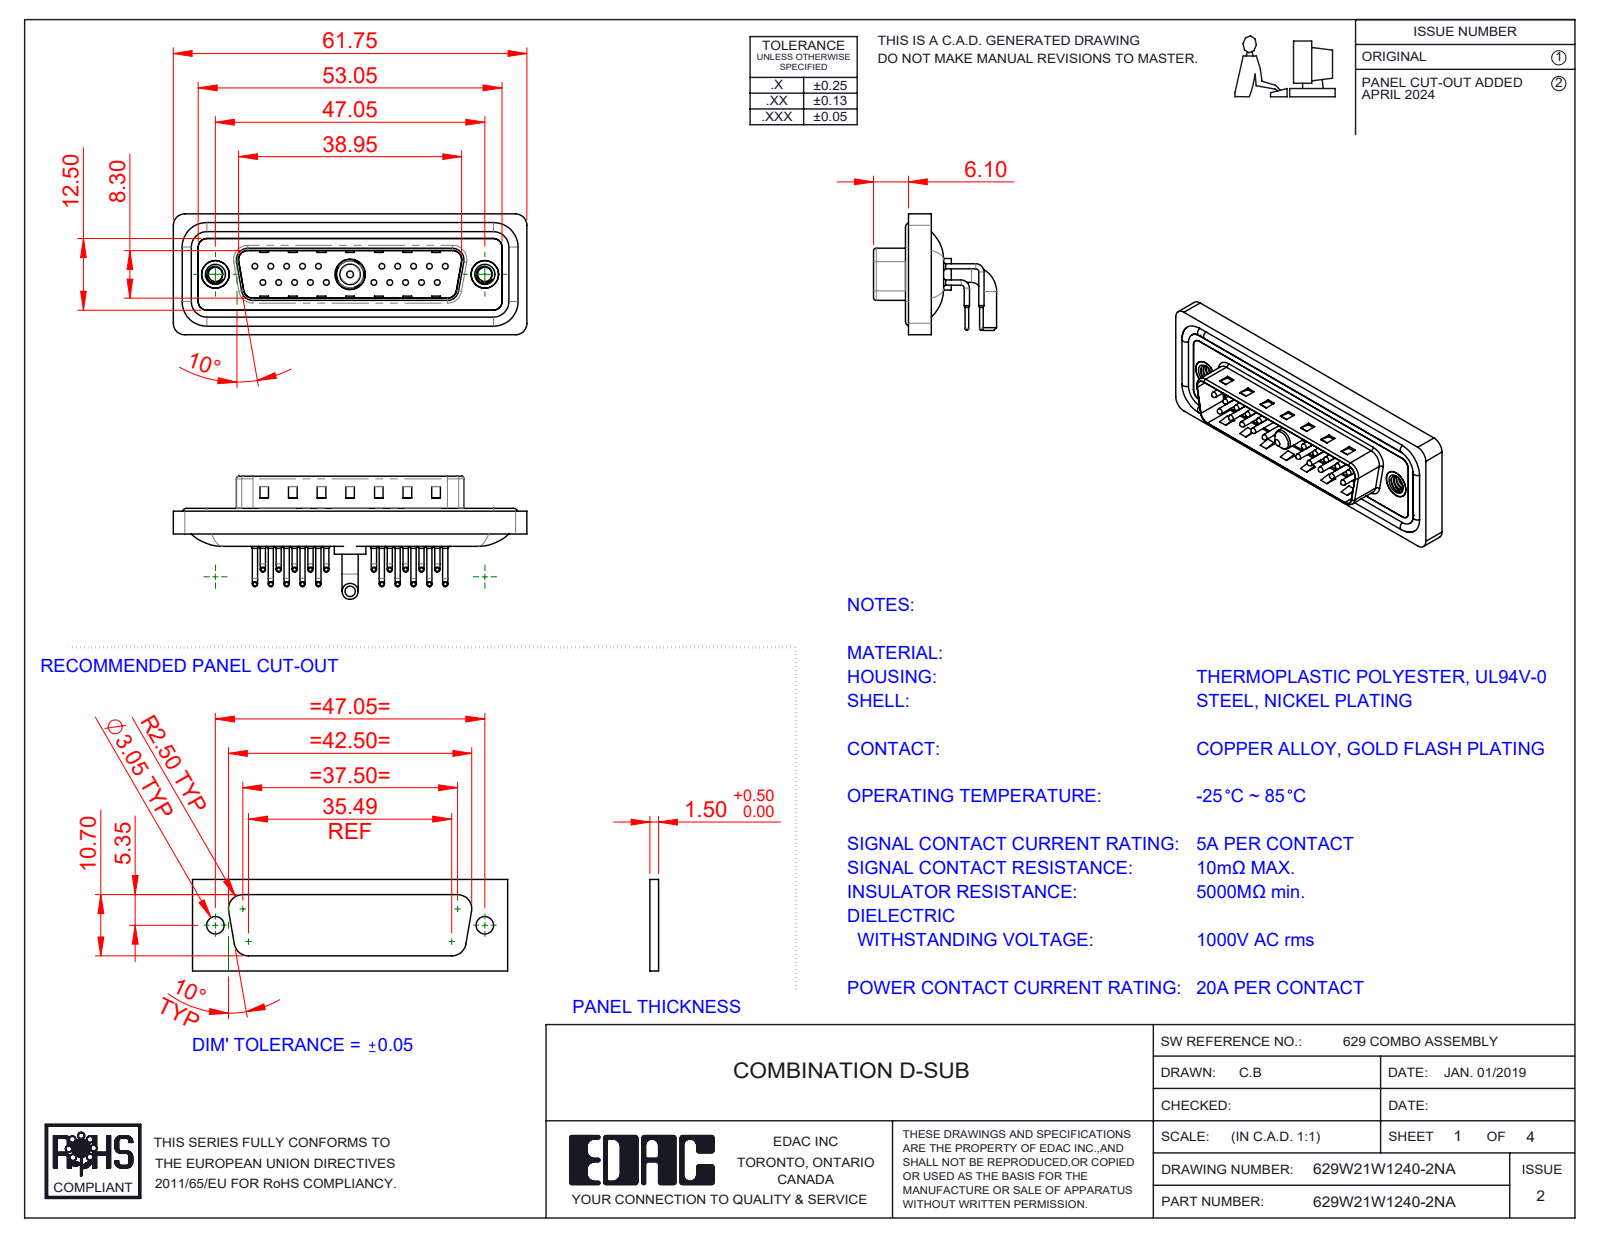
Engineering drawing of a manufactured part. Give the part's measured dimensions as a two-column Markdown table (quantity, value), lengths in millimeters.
| quantity | value |
| --- | --- |
| part name | 629Combo Contact Row 1; 629Combo Shell Rear_25 Contacts; 629W21W1240-2NA; 629Combo Shell Front_25 Contacts (+5 more) |
| STEP written by | SolidWorks 2023 (CONFIG_CONTROL_DESIGN) |
| units | millimeters |
| bodies | 29 solids, 2720 faces (1499 planar, 927 cylindrical, 294 other) |
| overall size | 61.75 × 21.5 × 21.1 |
| volume | 7 421 mm³ |
| surface area | 12 724 mm² |
| round holes (diameter × count) | 0.75 × 20, 1.6 × 20, 2 × 20, 2.5 × 2, 4 × 2, 4.8 × 2, 5 × 2, 4.85 × 1, 5.3 × 1 |
| round bosses / shafts (diameter × count) | 0.9 × 40, 1.5 × 20, 1 × 20, 0.65 × 20, 1.6 × 4, 4.9 × 2, 2.8 × 2, 5.5 × 1 |
| partial cylindrical surfaces (radius × count) | 1.01 × 20, 1.5 × 18, 2 × 18, 0.5 × 8, 1.6 × 8, 0.25 × 4, 0.6 × 4, 0.65 × 4 |
| main face-to-face distances | 0.4, 2.9, 0.8, 4.1, 1.1, 2.1, 1.6, 4.5, 1.5, 2.5 |
| hole center spacings | 3.16, 2.77, 5.54, 8.31, 5.04, 19.39, 20.97, 22.16 |
